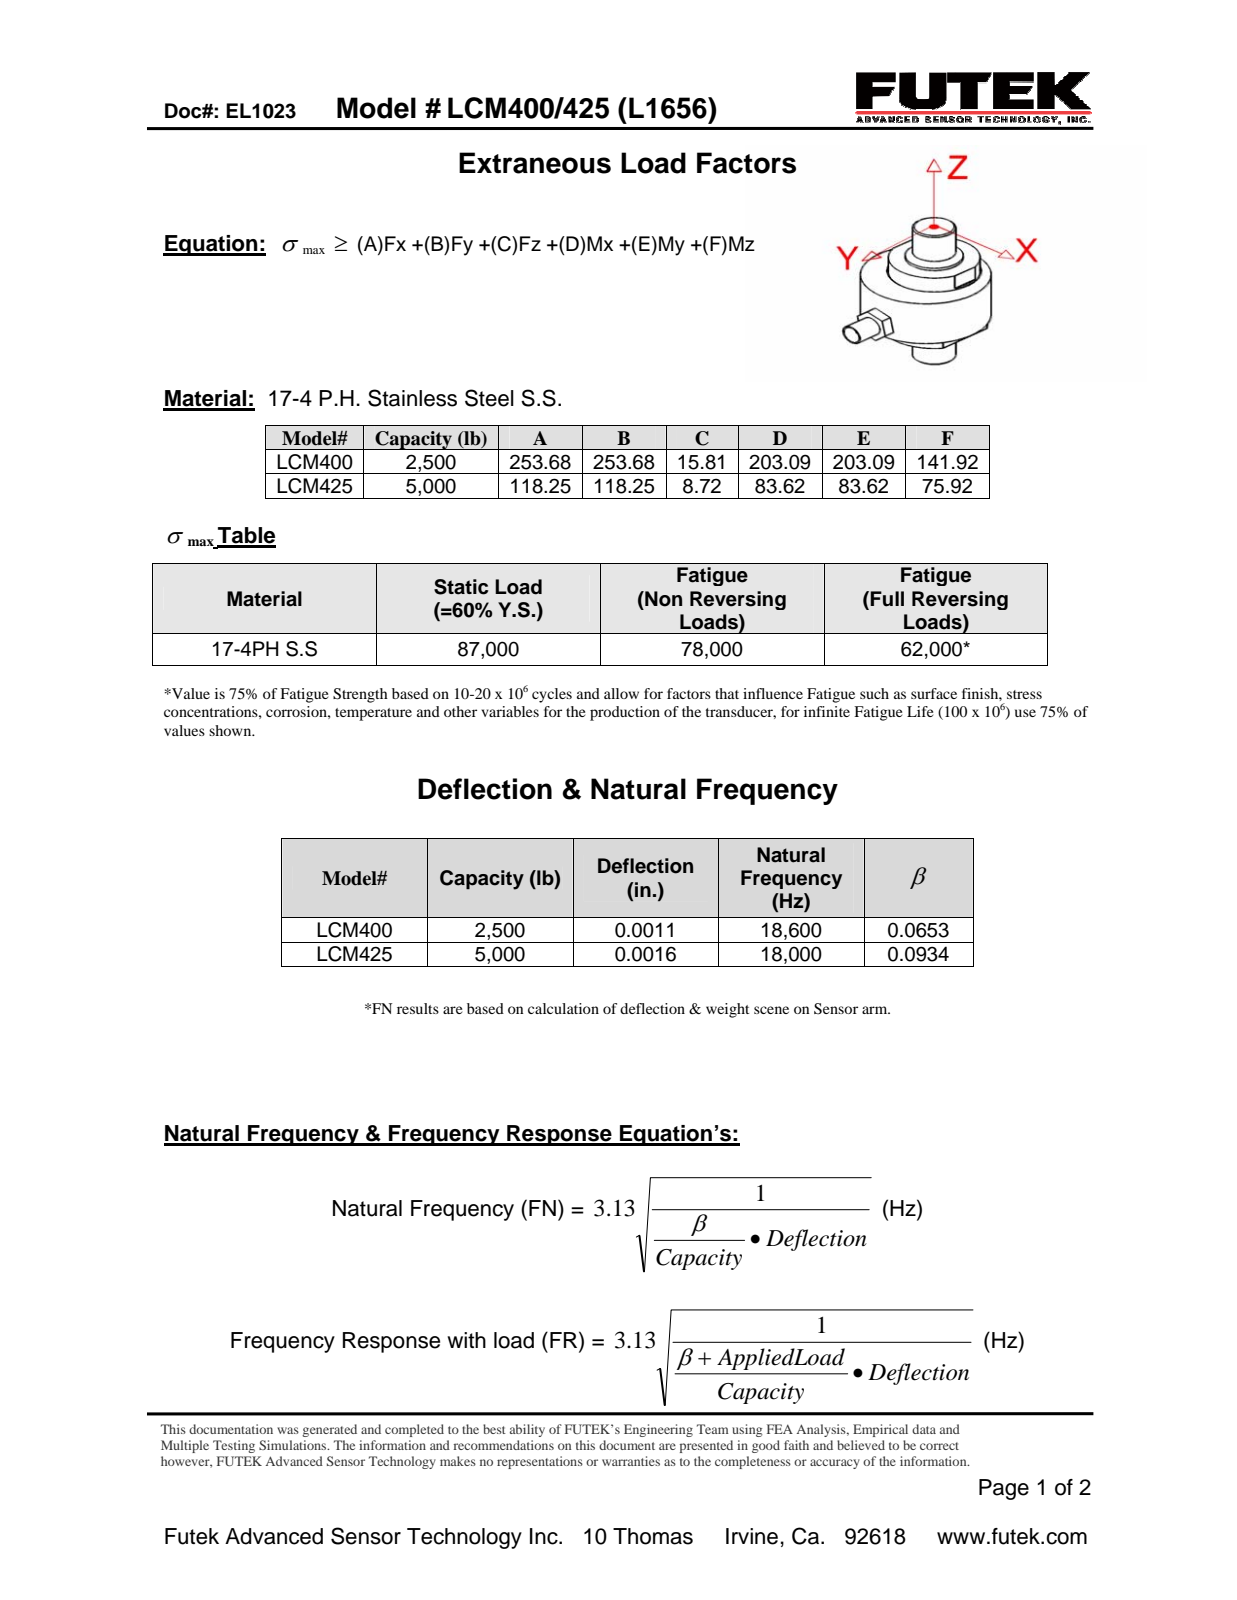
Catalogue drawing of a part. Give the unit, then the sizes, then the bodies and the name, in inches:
Units: inches
Overall size (bounding box): 1.75 × 1.465 × 1.125
Round holes (diameter × count): ⌀0.182 ×1, ⌀0.246 ×1, ⌀0.812 ×1
Round bosses / shafts (diameter × count): ⌀0.037 ×4, ⌀0.018 ×4, ⌀1.125 ×1, ⌀0.92 ×1, ⌀0.81 ×1, ⌀0.79 ×1, ⌀0.5 ×1, ⌀0.375 ×1
Main face-to-face distances: 0.73, 0.19, 0.54, 0.72, 0.91, 0.18, 0.75, 0.42, 1.33, 0.03
Volume: 0.83 in³ · Surface area: 9.515 in²
Bodies: 1 solid, 62 faces (33 planar, 21 cylindrical, 8 other)
Part name (STEP PRODUCT): LCM400; $F1742
STEP written by: Autodesk Inventor 2008 (AUTOMOTIVE_DESIGN)
